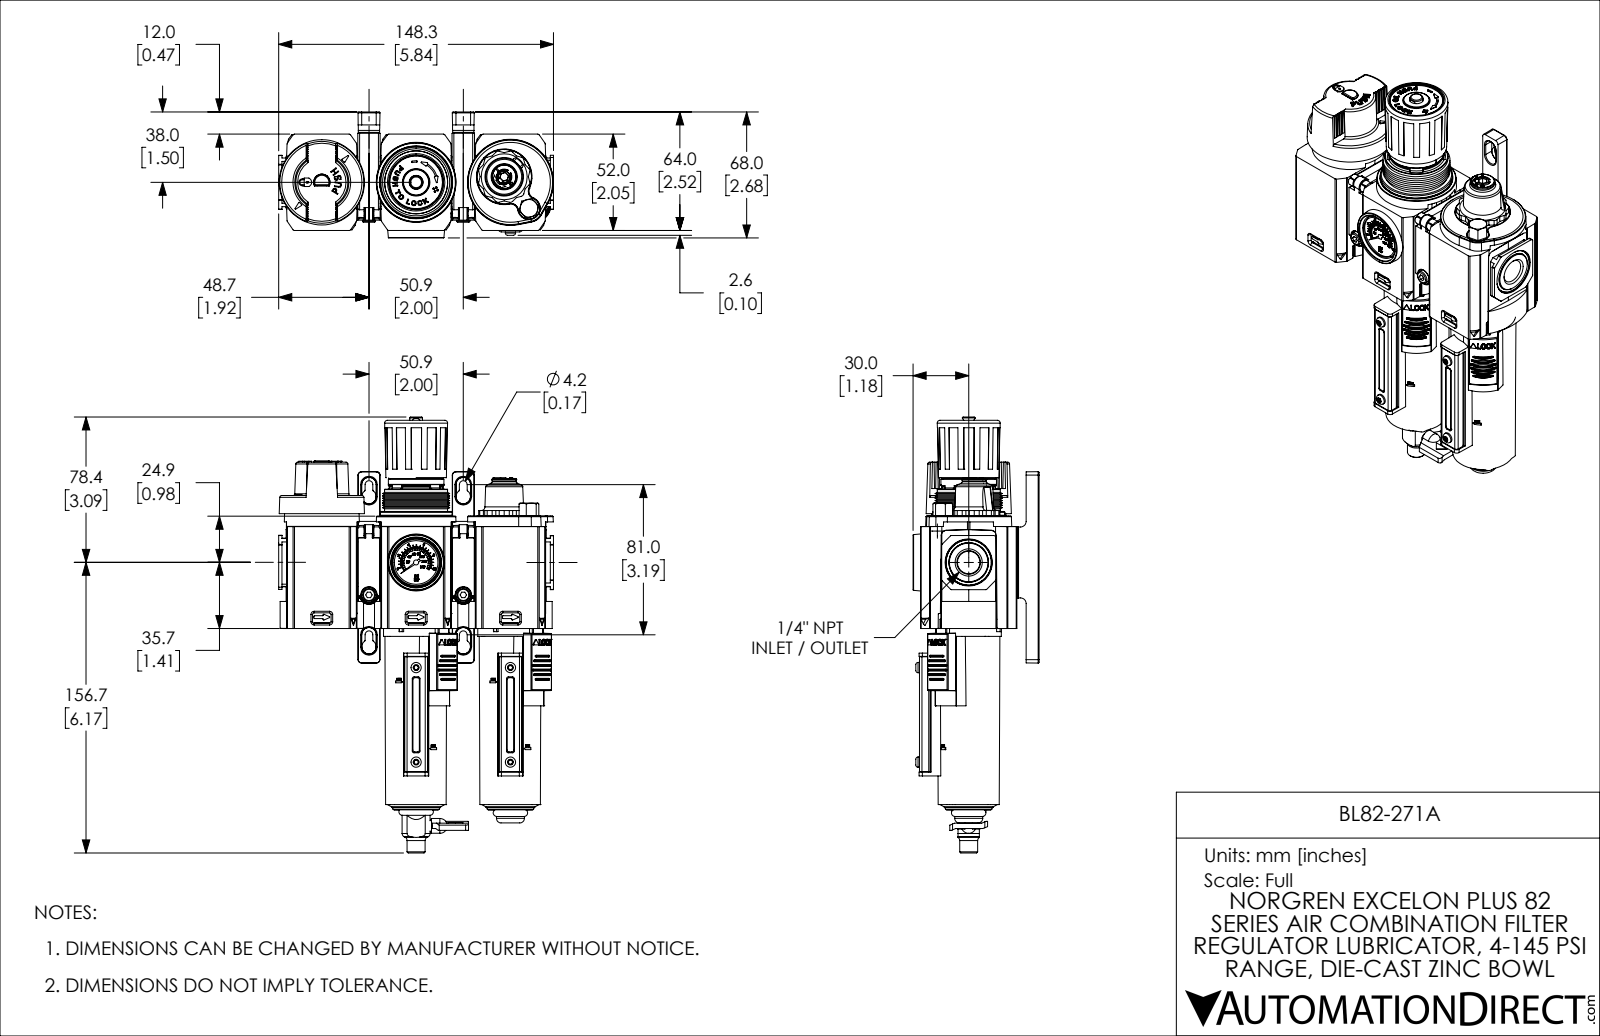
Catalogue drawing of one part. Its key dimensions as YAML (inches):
part_name: "BL82-271A"
step_written_by: "SolidWorks 2021 (CONFIG_CONTROL_DESIGN)"
units: inches
bodies: {solids: 20, faces: 5439, planar: 2310, cylindrical: 2179, other: 950}
overall_size: [9.257, 5.839, 2.676]
volume: 37.85
surface_area: 329.2
round_holes:
  - {diameter: 0.097, count: 4}
  - {diameter: 0.306, count: 4}
  - {diameter: 0.039, count: 2}
  - {diameter: 0.128, count: 2}
  - {diameter: 0.138, count: 2}
  - {diameter: 0.175, count: 2}
  - {diameter: 0.187, count: 2}
  - {diameter: 0.628, count: 2}
  - {diameter: 0.106, count: 1}
  - {diameter: 0.128, count: 1}
  - {diameter: 0.197, count: 1}
  - {diameter: 0.199, count: 1}
round_bosses_or_shafts:
  - {diameter: 0.276, count: 4}
  - {diameter: 0.217, count: 4}
  - {diameter: 1.388, count: 2}
  - {diameter: 1.356, count: 2}
  - {diameter: 1.291, count: 2}
  - {diameter: 1.257, count: 2}
  - {diameter: 0.906, count: 2}
  - {diameter: 0.626, count: 2}
partial_cylinders:
  - {radius: 0.039, count: 152}
  - {radius: 0.02, count: 148}
  - {radius: 0.01, count: 27}
  - {radius: 0.006, count: 26}
  - {radius: 0.009, count: 25}
  - {radius: 0.011, count: 25}
  - {radius: 0.012, count: 25}
  - {radius: 0.03, count: 25}
face_to_face_distances: [0.059, 2.004, 1.988, 2.002, 2.047, 1.929, 4.004, 1.352, 0.182, 0.173]
hole_center_spacings: [0.63, 2.004, 0.554, 1.58, 0.59, 0.689, 1.002, 1.091]
